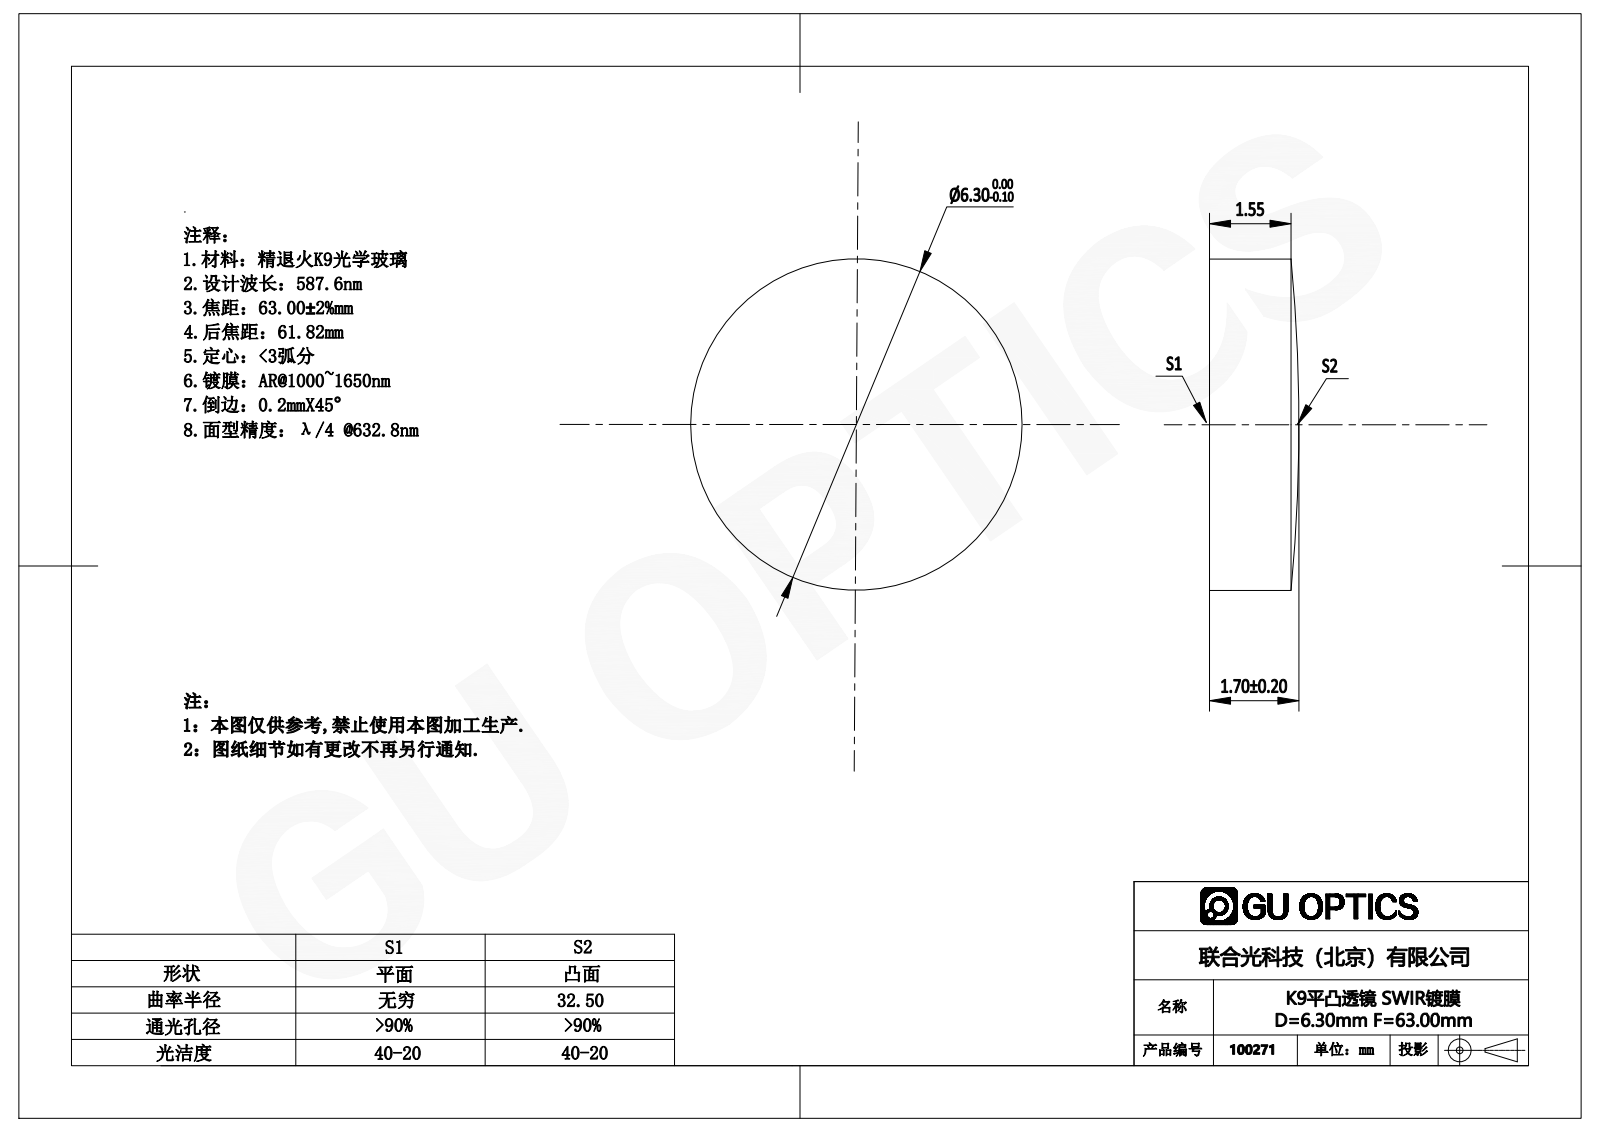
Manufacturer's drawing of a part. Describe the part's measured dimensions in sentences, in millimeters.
The part is named "100099". Its 3-D file was written by "SolidWorks 2016 (AUTOMOTIVE_DESIGN)". It is 1 solid with 5 faces: 1 planar, 2 cylindrical and 2 other. Overall it measures 6.3 by 6.3 by 1.7 millimeters. Its volume is 51 cubic millimeters and its surface area 93 square millimeters. Round bosses or shafts: 1 of diameter 6.3.
